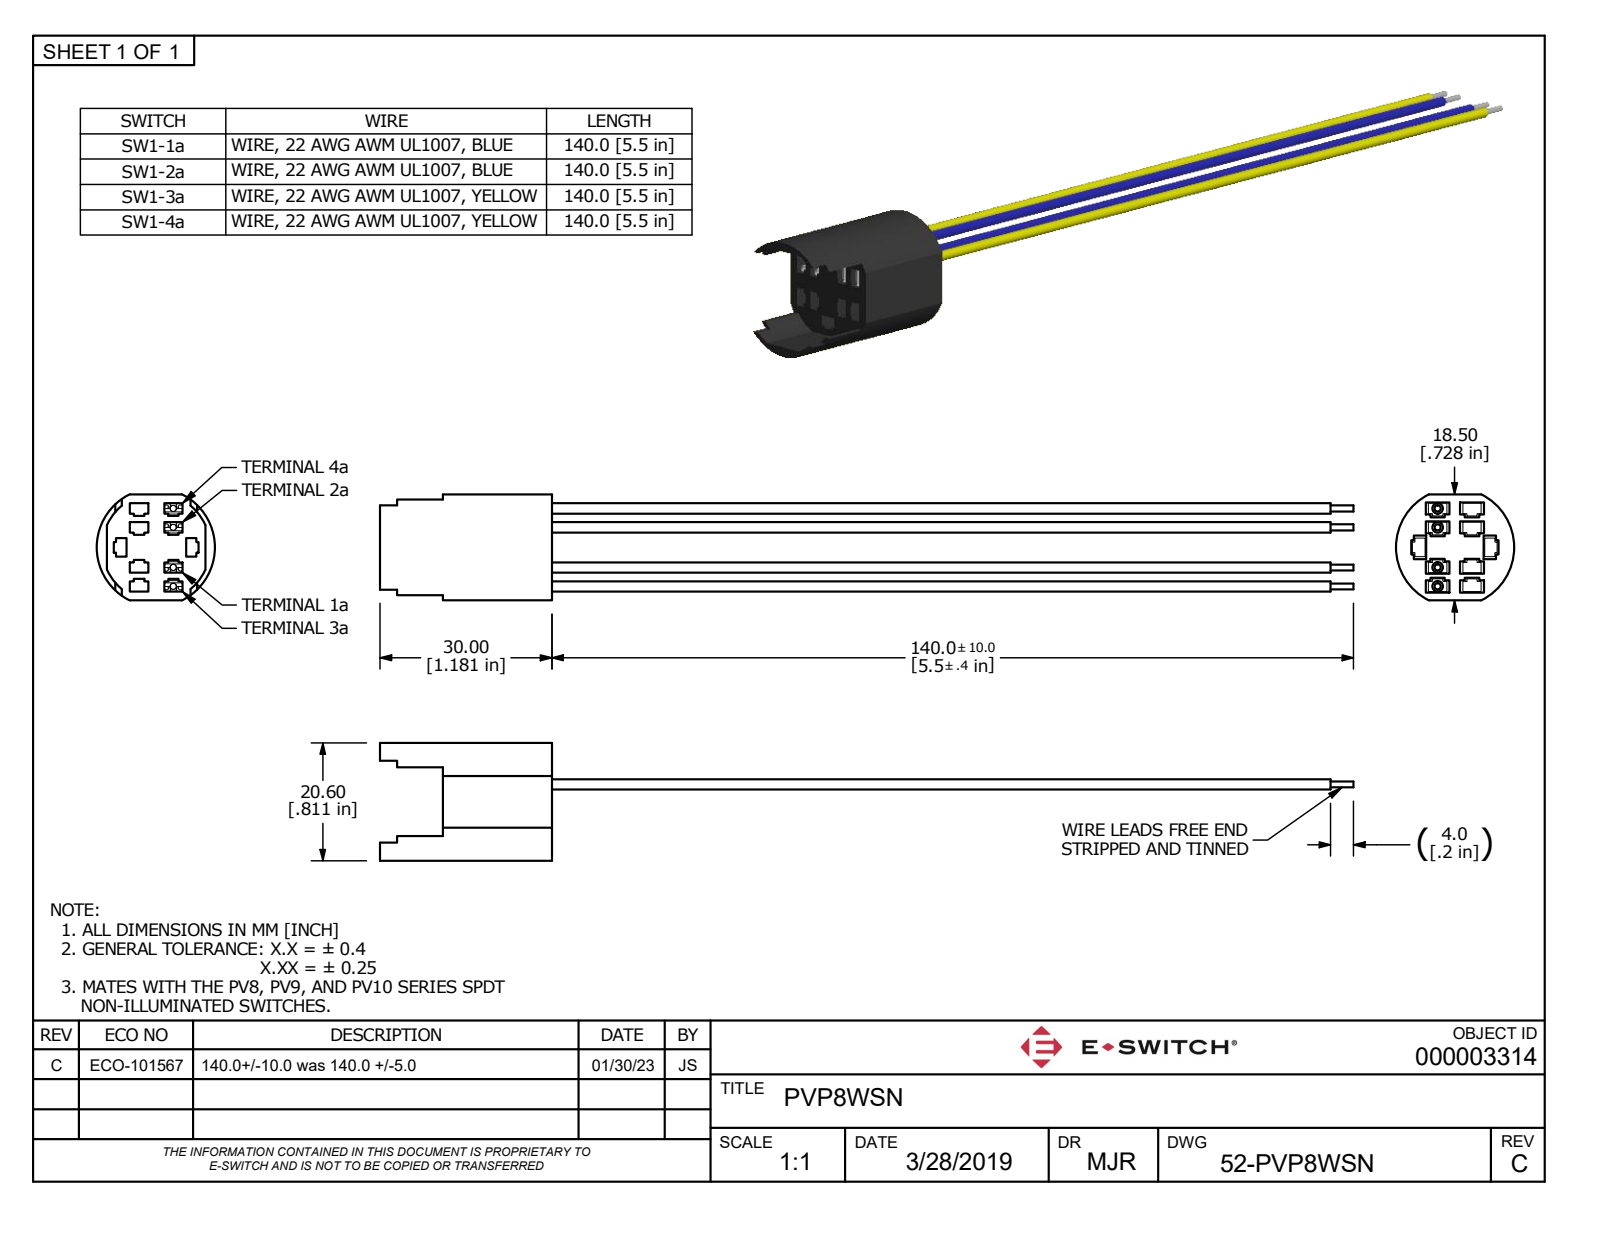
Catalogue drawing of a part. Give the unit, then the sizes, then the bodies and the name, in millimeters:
Units: millimetres
Overall size (bounding box): 170 × 20.6 × 18.5
Round bosses / shafts (diameter × count): ⌀1.8 ×4
Partial cylindrical surfaces — rounded edges, fillets, slot ends (radius × count): R0.25 ×24, R0.5 ×8, R0.52 ×4, R9.45 ×1, R10.3 ×1
Main face-to-face distances: 3.3, 12.27, 6, 19, 13.2, 2.2, 2.37, 3.67, 2.8, 3.2
Volume: 6 586 mm³ · Surface area: 8 382 mm²
Bodies: 1 solid, 368 faces (294 planar, 50 cylindrical, 24 other)
Part name (STEP PRODUCT): PVP8WSN
STEP written by: Autodesk Inventor 2018 (AP242_MANAGED_MODEL_BASED_3D_ENGINEERING_MIM_LF)
